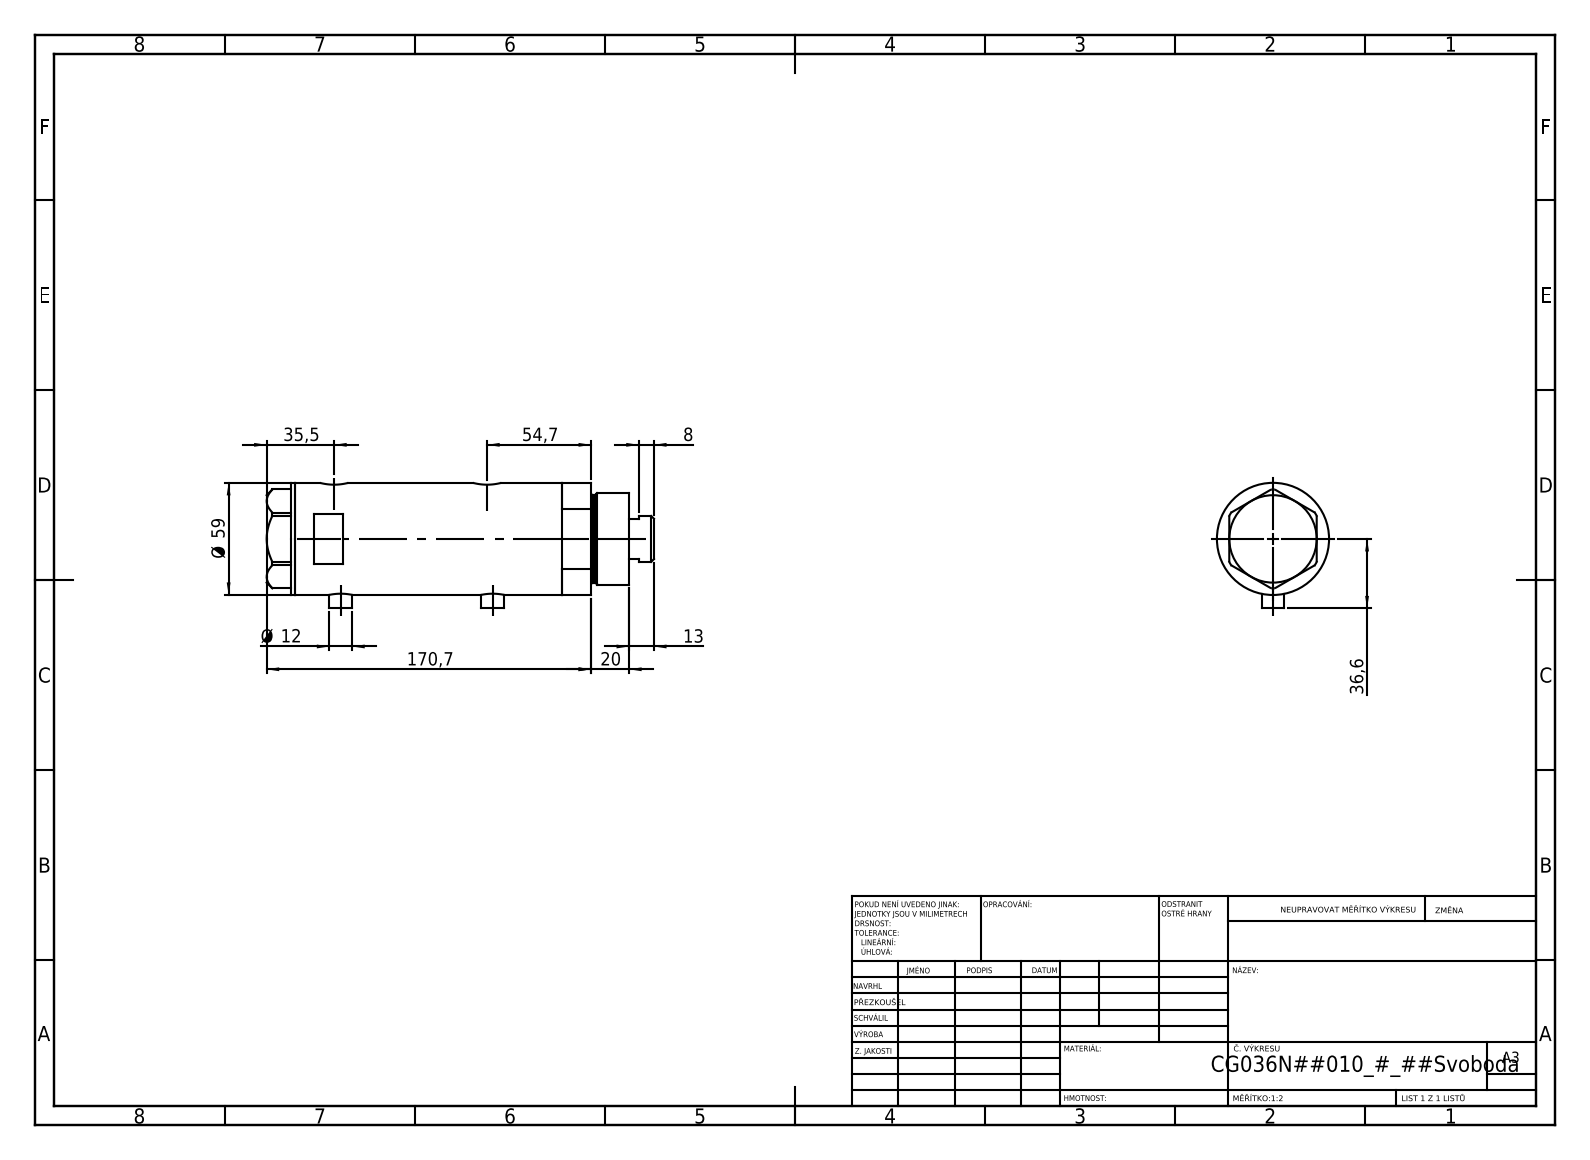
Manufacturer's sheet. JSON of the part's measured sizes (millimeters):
{"part_name": "V270CG_FRONT; V270CG_MIDDLE; V270CG_BACK; V270CG_VC", "step_written_by": "SolidWorks 2019 (CONFIG_CONTROL_DESIGN)", "units": "millimeters", "bodies": {"solids": 4, "faces": 126, "planar": 53, "cylindrical": 53, "other": 20}, "overall_size": [203.8, 66.1, 59], "volume_mm3": 483027, "surface_area_mm2": 99640, "round_holes": [[5, 2], [9.73, 2], [12.5, 2], [15, 2], [8.5, 1], [25, 1], [26.5, 1], [36, 1], [40, 1], [52, 1]], "round_bosses_or_shafts": [[12, 2], [59, 1], [48, 1], [46, 1], [24, 1]], "face_to_face_distances": [102.2, 23.5, 78.7, 15, 38.5, 117.2, 2, 175.7, 190.7, 152.2], "hole_center_spacings": [2.9, 3.5, 77, 79.9, 80.5, 83.4]}
